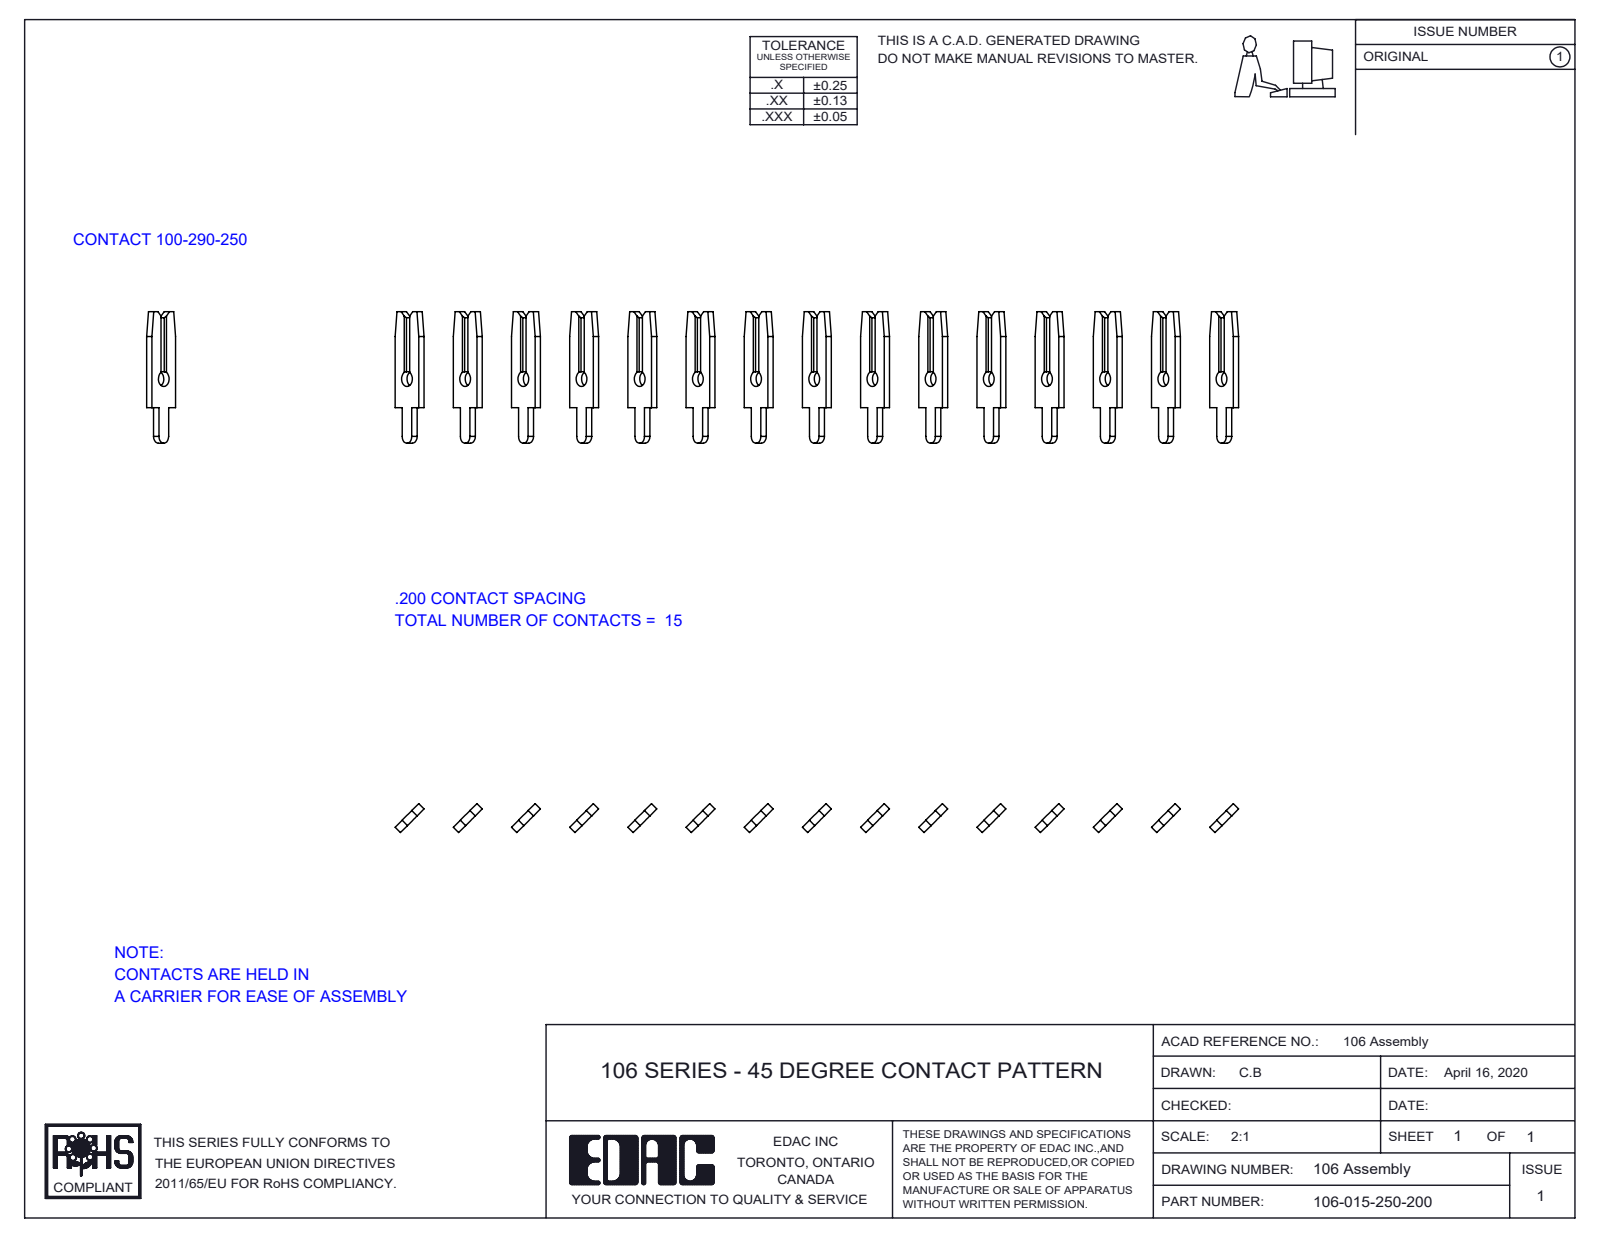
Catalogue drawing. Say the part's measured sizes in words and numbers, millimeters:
The part is named "106-015-250-200; 100-290-001_100-290-250". Its 3-D file was written by "SolidWorks 2016 (CONFIG_CONTROL_DESIGN)". It is 15 solids with 360 faces: 300 planar, 60 cylindrical and 0 other. Overall it measures 73.7 by 11.5 by 2.5 millimeters. Its volume is 230 cubic millimeters and its surface area 1 100 square millimeters. Round holes: 15 of diameter 1.3. Partial cylindrical surfaces (rounded edges, fillets, slot ends): 15 of radius 0.6. The main face-to-face distances are 3.6, 7.2, 18, 21.5, 14.4, 10.8, 25.1, 10.8, 28.7, 18.6. The hole center spacings are 3.6, 7.2, 10.8, 21.5, 14.4, 25.1, 18, 28.7.
